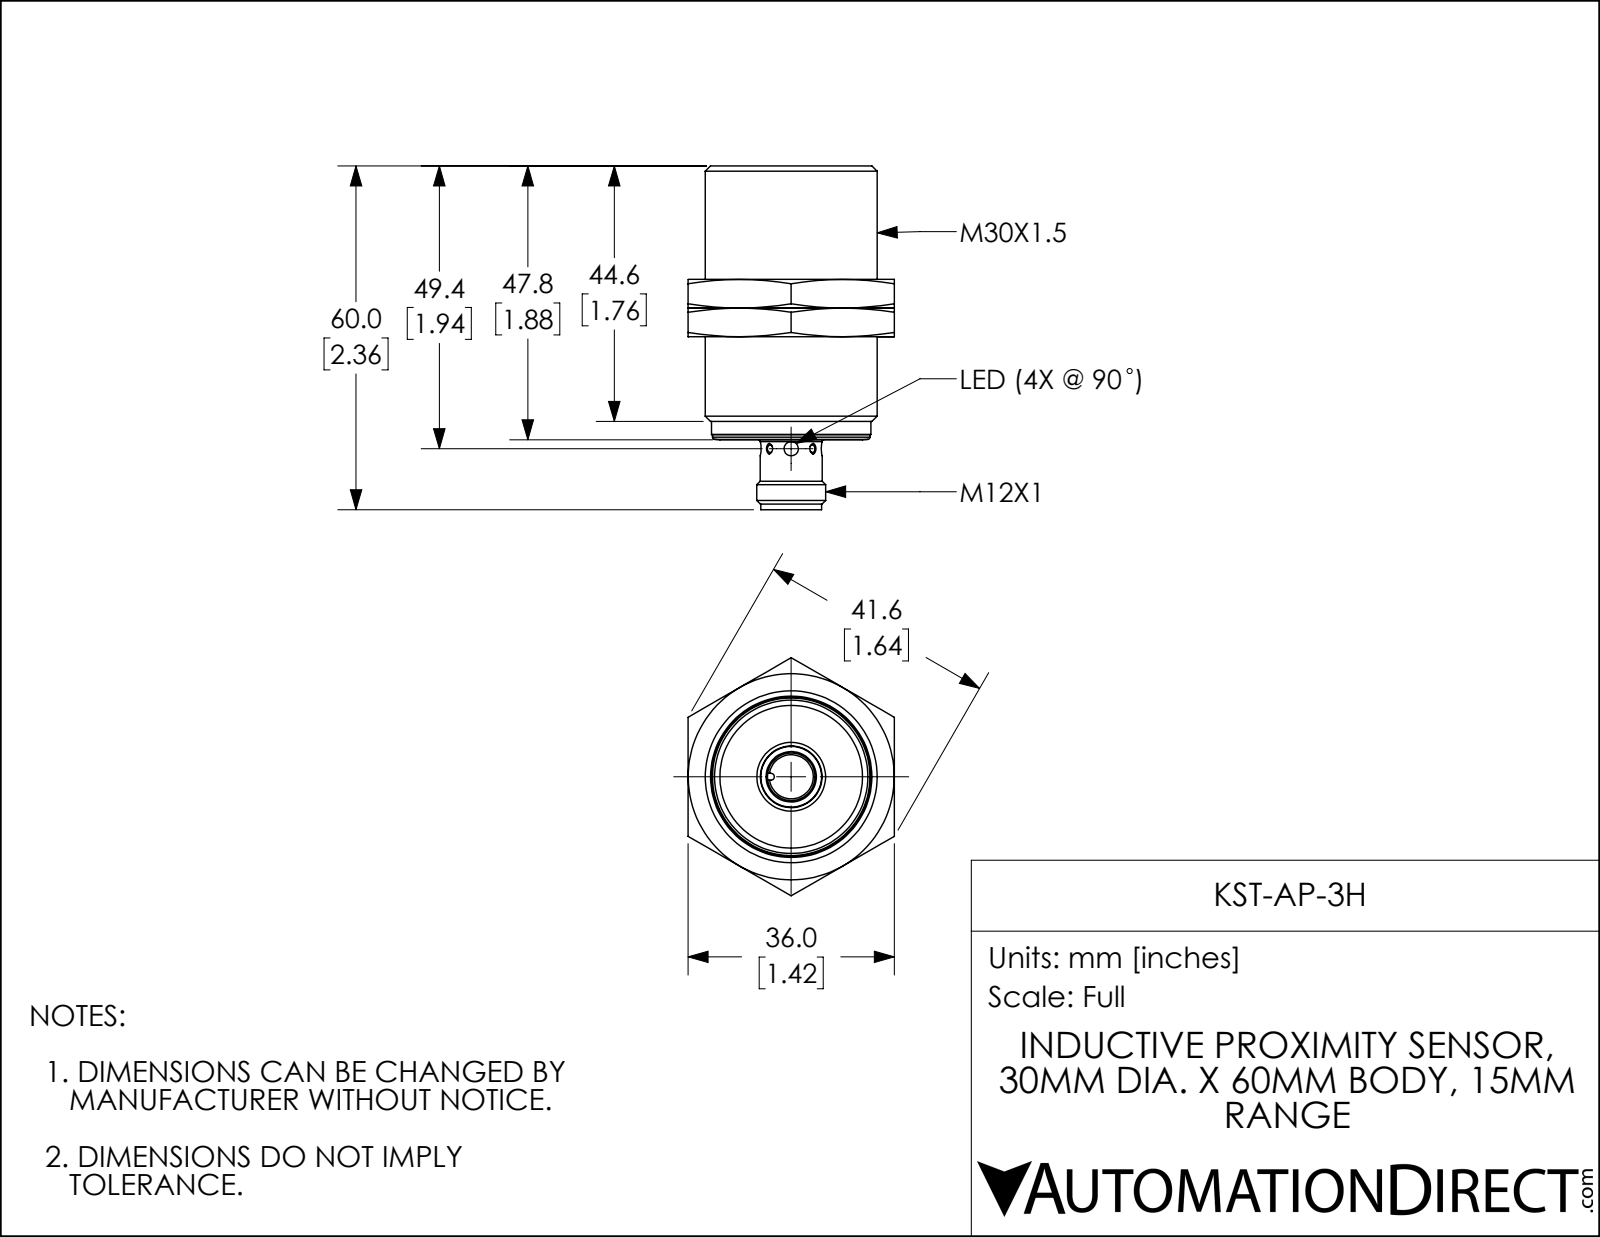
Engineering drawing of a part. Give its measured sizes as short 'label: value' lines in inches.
name: KST-AP-3H
written by: SolidWorks 2017 (AUTOMOTIVE_DESIGN)
unit: in
bodies: 3 solids, 74 faces (27 planar, 20 cylindrical, 27 other)
size: 2.362 × 1.637 × 1.417
volume: 2.369 in³; area: 16.22 in²
holes: 2× ⌀0.098, 1× ⌀0.327, 1× ⌀1.076, 1× ⌀1.117
bosses: 1× ⌀1.181, 1× ⌀1.094, 1× ⌀1.083, 1× ⌀1.074, 1× ⌀0.472, 1× ⌀0.425, 1× ⌀0.417
rounds: 1× R0.024, 1× R0.185
face distances: 0.976, 0.197, 1.417, 0.906, 1.882, 0.78, 0.709, 1.173, 1.102, 0.394
